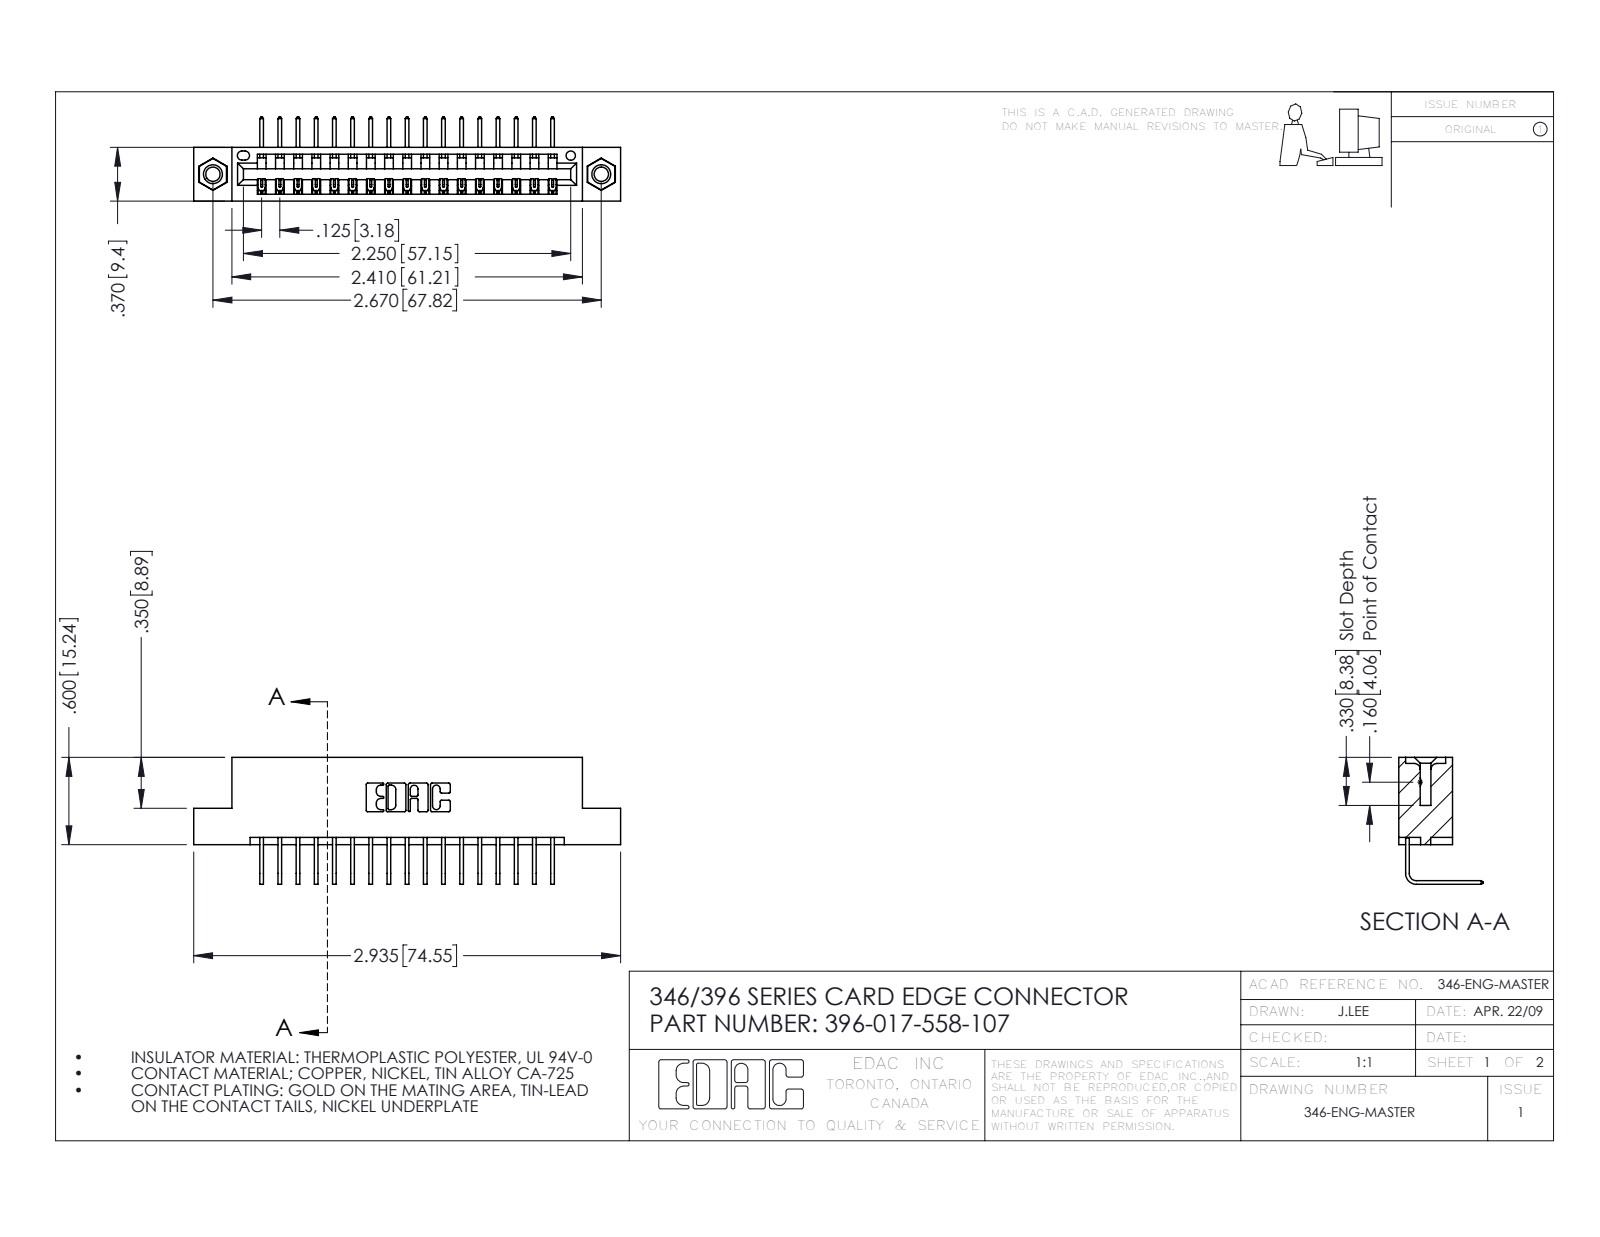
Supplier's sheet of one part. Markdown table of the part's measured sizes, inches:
| quantity | value |
| --- | --- |
| part name | 396-017-558-107; 345-250-001_345-250-005-103; 345-292-001_558 Tail - 2; 346 Part_Flush Mounting Lugs - 0.156 Dia-TI |
| STEP written by | SolidWorks 2016 (CONFIG_CONTROL_DESIGN) |
| units | inches |
| bodies | 20 solids, 1202 faces (822 planar, 364 cylindrical, 16 other) |
| overall size | 2.935 × 0.873 × 0.58 |
| volume | 0.428 in³ |
| surface area | 13.73 in² |
| round holes (diameter × count) | 0.098 × 2, 0.125 × 2, 0.156 × 2, 0.064 × 1 |
| round bosses / shafts (diameter × count) | 0.155 × 2 |
| partial cylindrical surfaces (radius × count) | 0.006 × 34, 0.01 × 22, 0.007 × 6, 0.031 × 6, 0.026 × 3, 0.031 × 2, 0.04 × 2, 0.014 × 1 |
| main face-to-face distances | 0.322, 0.048, 0.25, 0.37, 0.298, 0.025, 0.072, 0.148, 0.222, 0.1 |
| hole center spacings | 0.246, 2.463, 2.67 |
